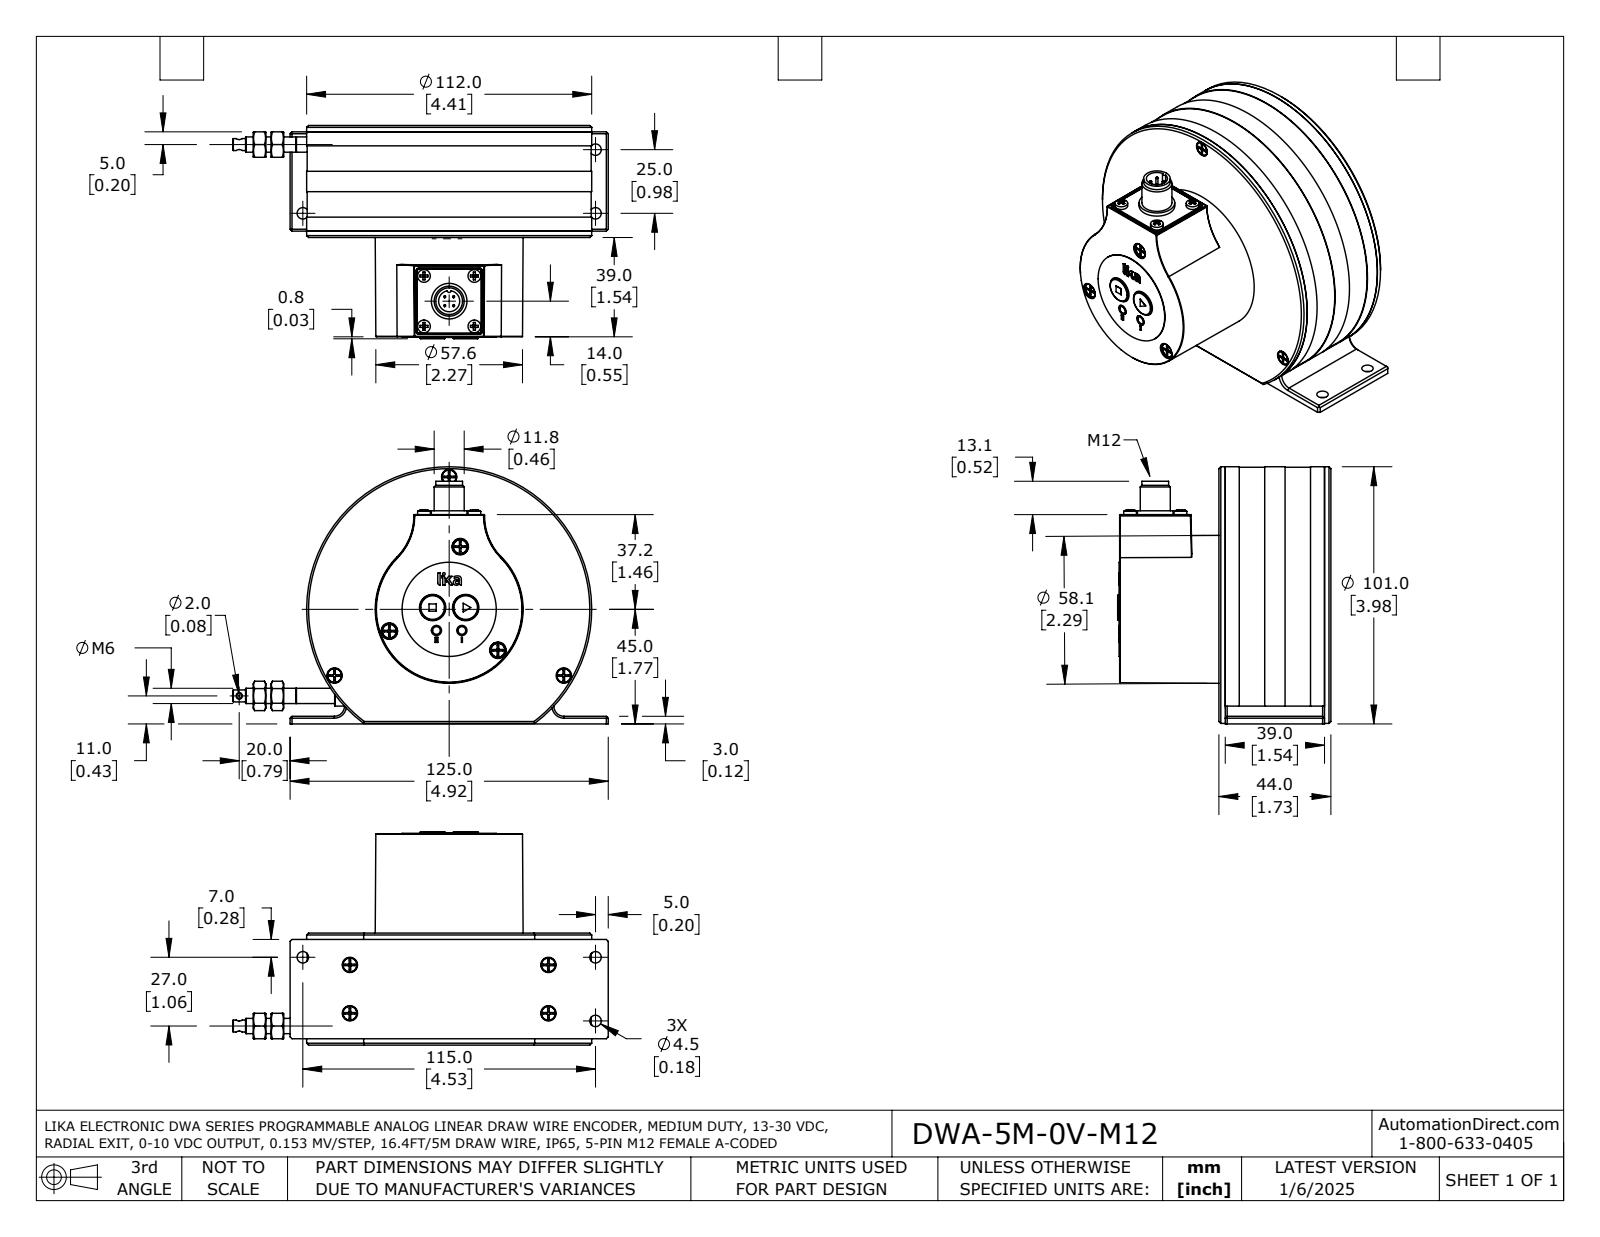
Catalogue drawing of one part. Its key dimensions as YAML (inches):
part_name: "DWA-5M-0V-M12"
step_written_by: "SolidWorks 2021 (AUTOMOTIVE_DESIGN)"
units: inches
bodies: {solids: 31, faces: 2026, planar: 1231, cylindrical: 397, other: 398}
overall_size: [5.807, 3.976, 3.299]
volume: 12.98
surface_area: 185.4
round_holes:
  - {diameter: 0.098, count: 13}
  - {diameter: 0.126, count: 7}
  - {diameter: 0.236, count: 7}
  - {diameter: 0.079, count: 5}
  - {diameter: 0.157, count: 4}
  - {diameter: 0.177, count: 4}
  - {diameter: 0.059, count: 2}
  - {diameter: 0.063, count: 2}
  - {diameter: 0.118, count: 2}
  - {diameter: 0.315, count: 2}
  - {diameter: 0.374, count: 2}
  - {diameter: 0.197, count: 1}
round_bosses_or_shafts:
  - {diameter: 0.118, count: 11}
  - {diameter: 0.197, count: 4}
  - {diameter: 0.098, count: 4}
  - {diameter: 0.055, count: 4}
  - {diameter: 0.031, count: 4}
  - {diameter: 0.157, count: 2}
  - {diameter: 4.409, count: 1}
  - {diameter: 2.205, count: 1}
partial_cylinders:
  - {radius: 0.008, count: 45}
  - {radius: 0.007, count: 33}
  - {radius: 0.02, count: 6}
  - {radius: 0.03, count: 5}
  - {radius: 0.157, count: 2}
  - {radius: 0.034, count: 1}
  - {radius: 0.035, count: 1}
  - {radius: 0.036, count: 1}
face_to_face_distances: [0.02, 1.634, 0.098, 0.079, 1.535, 0.118, 1.654, 1.319, 1.732, 0.059]
hole_center_spacings: [0.984, 1.705, 0.648, 0.738, 0.509, 0.728, 0.827, 1.039]
